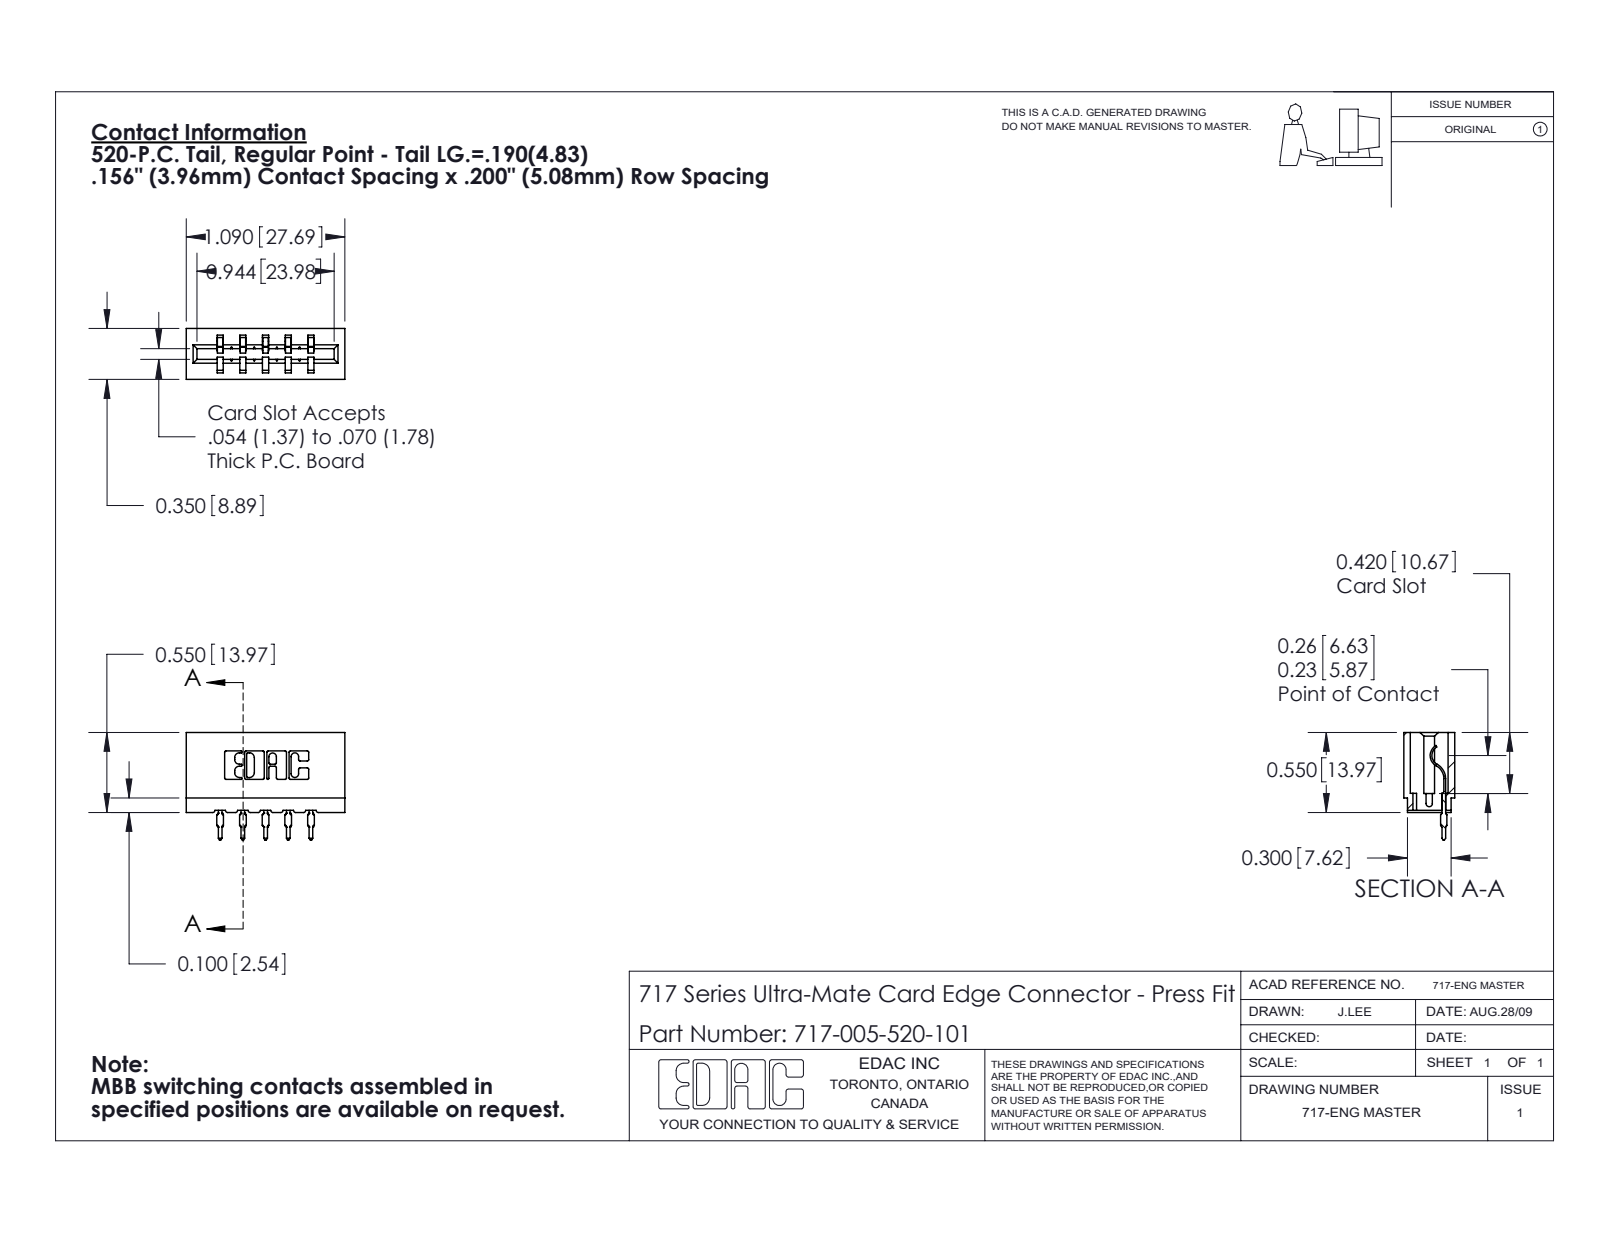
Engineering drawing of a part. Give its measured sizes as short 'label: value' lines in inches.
name: 717-005-520-101; 745-292-001_520; 717 Part_Insulator Option - 06
written by: SolidWorks 2020 (CONFIG_CONTROL_DESIGN)
unit: in
bodies: 6 solids, 659 faces (394 planar, 135 cylindrical, 130 other)
size: 1.09 × 0.739 × 0.35
volume: 0.152 in³; area: 4.762 in²
rounds: 22× R0.01, 10× R0.015, 10× R0.021, 6× R0.007, 6× R0.031, 4× R0.005, 4× R0.011, 3× R0.026
face distances: 0.212, 0.156, 0.138, 0.35, 0.198, 0.042, 0.312, 0.468, 0.312, 0.074
